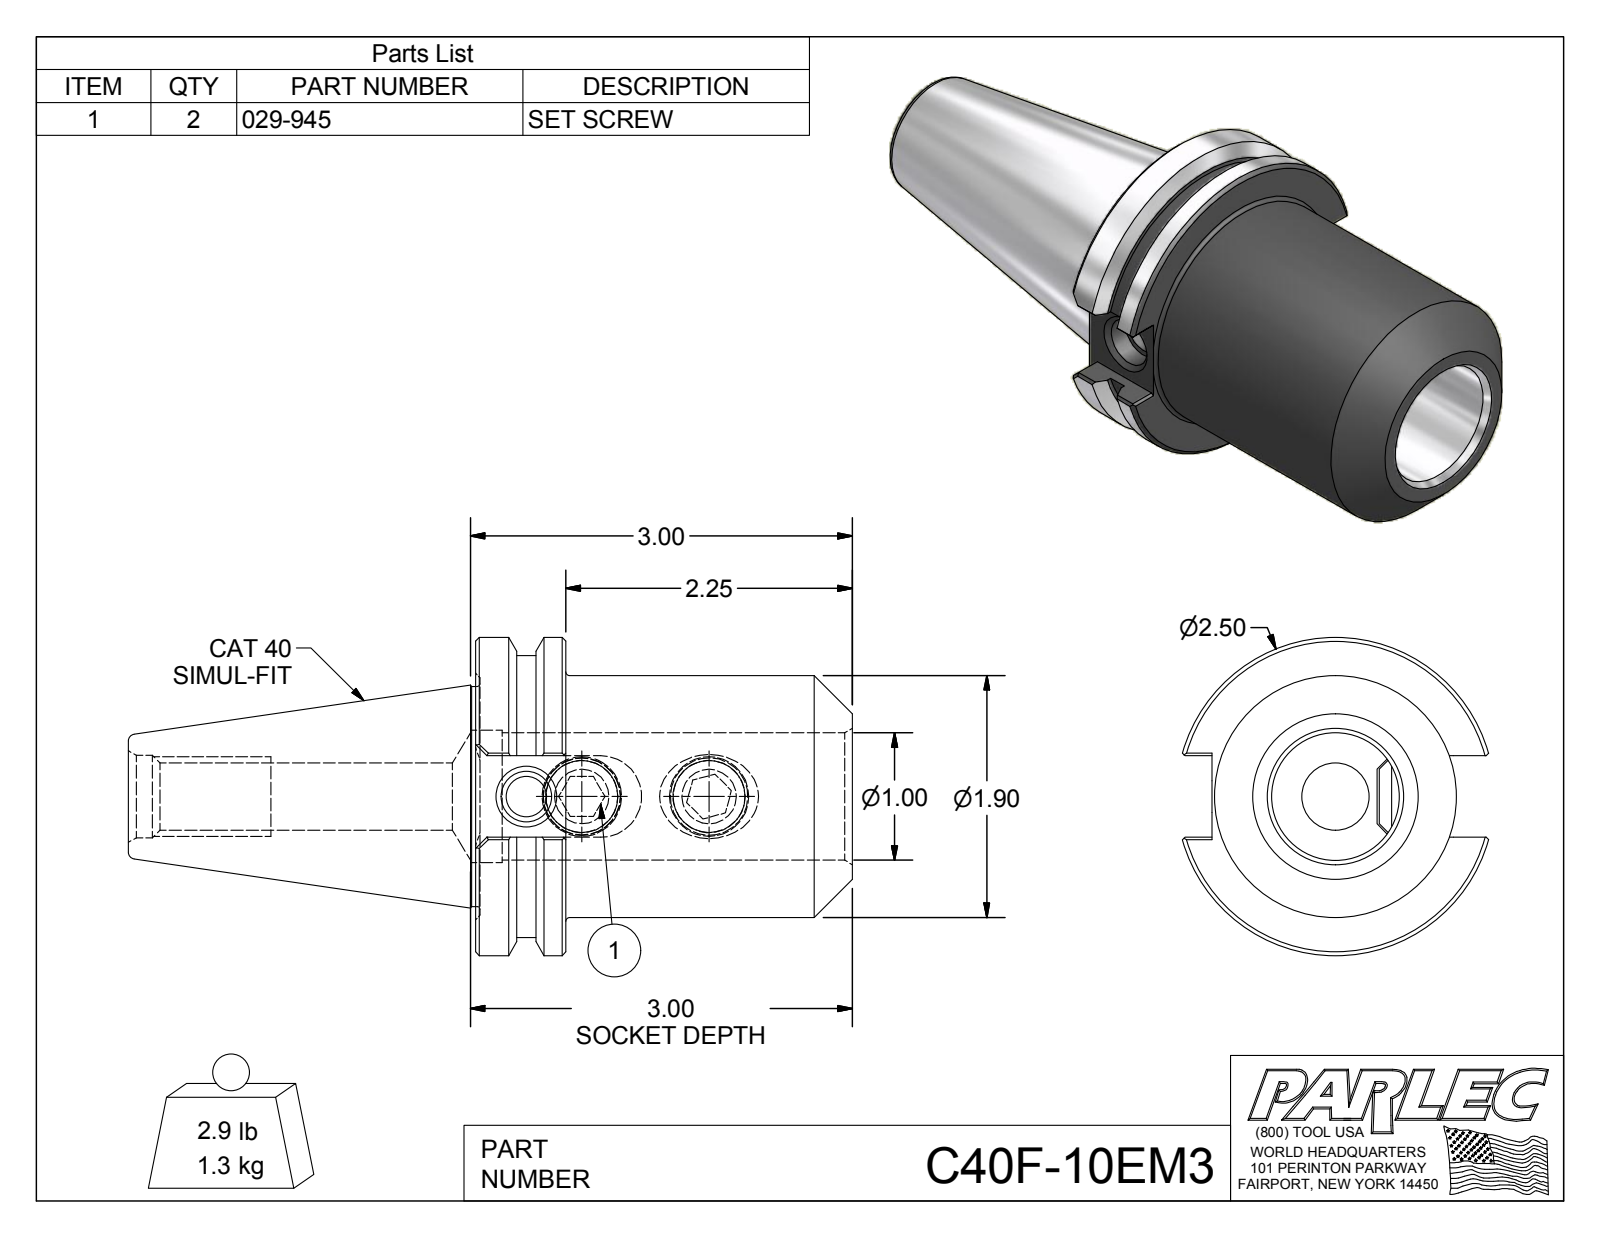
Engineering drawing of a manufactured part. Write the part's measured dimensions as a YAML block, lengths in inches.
part_name: "C40F-10EM3; C40F-10EM3-1; 029-945"
step_written_by: "Autodesk Inventor 2012 (AUTOMOTIVE_DESIGN)"
units: inches
bodies: {solids: 3, faces: 101, planar: 51, cylindrical: 19, other: 31}
overall_size: [5.688, 2.5, 2.406]
volume: 10.18
surface_area: 56.3
round_holes:
  - {diameter: 0.565, count: 2}
  - {diameter: 0.315, count: 1}
  - {diameter: 0.399, count: 1}
  - {diameter: 0.527, count: 1}
  - {diameter: 0.648, count: 1}
  - {diameter: 1, count: 1}
  - {diameter: 1.04, count: 1}
round_bosses_or_shafts:
  - {diameter: 0.625, count: 2}
  - {diameter: 2.5, count: 1}
  - {diameter: 2.215, count: 1}
  - {diameter: 1.9, count: 1}
  - {diameter: 1.73, count: 1}
partial_cylinders:
  - {radius: 0.32, count: 1}
face_to_face_distances: [0.711, 0.018, 2.961, 2.25, 0.5, 1.86, 0.315, 0.64, 0.037, 0.674]
hole_center_spacings: [0.435, 1, 1.435]
